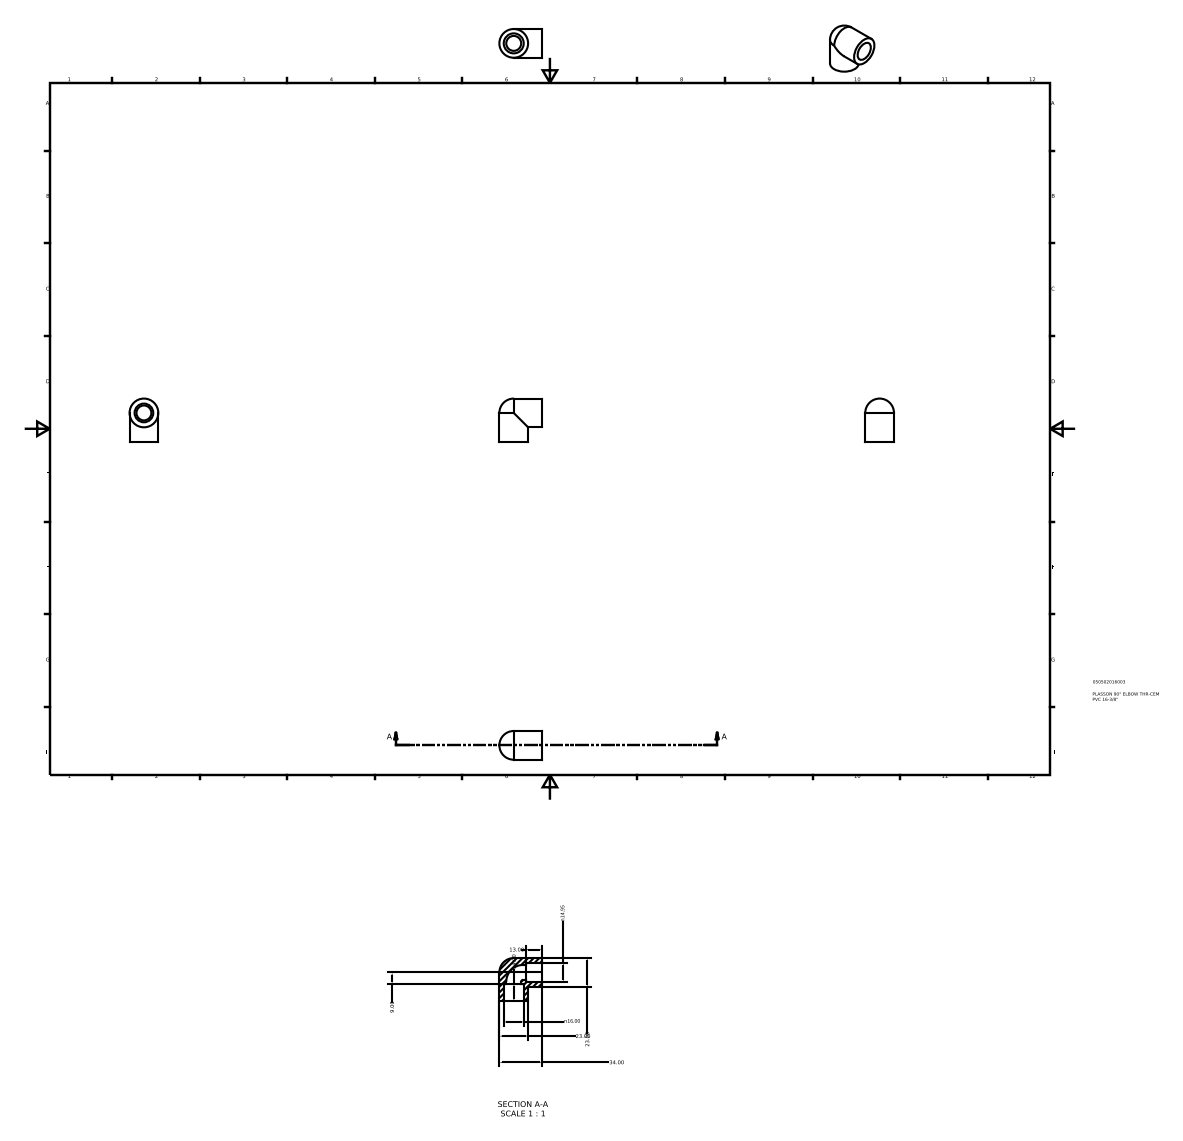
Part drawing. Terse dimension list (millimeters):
name: 050502016003
written by: Autodesk Inventor 2015 (AUTOMOTIVE_DESIGN)
unit: mm
bodies: 1 solid, 12 faces (4 planar, 6 cylindrical, 2 other)
size: 34.5 × 34 × 23
volume: 11 654 mm³; area: 5 669 mm²
holes: 2× ⌀11.96, 1× ⌀14.95, 1× ⌀16
bosses: 2× ⌀23
face distances: 14, 13
